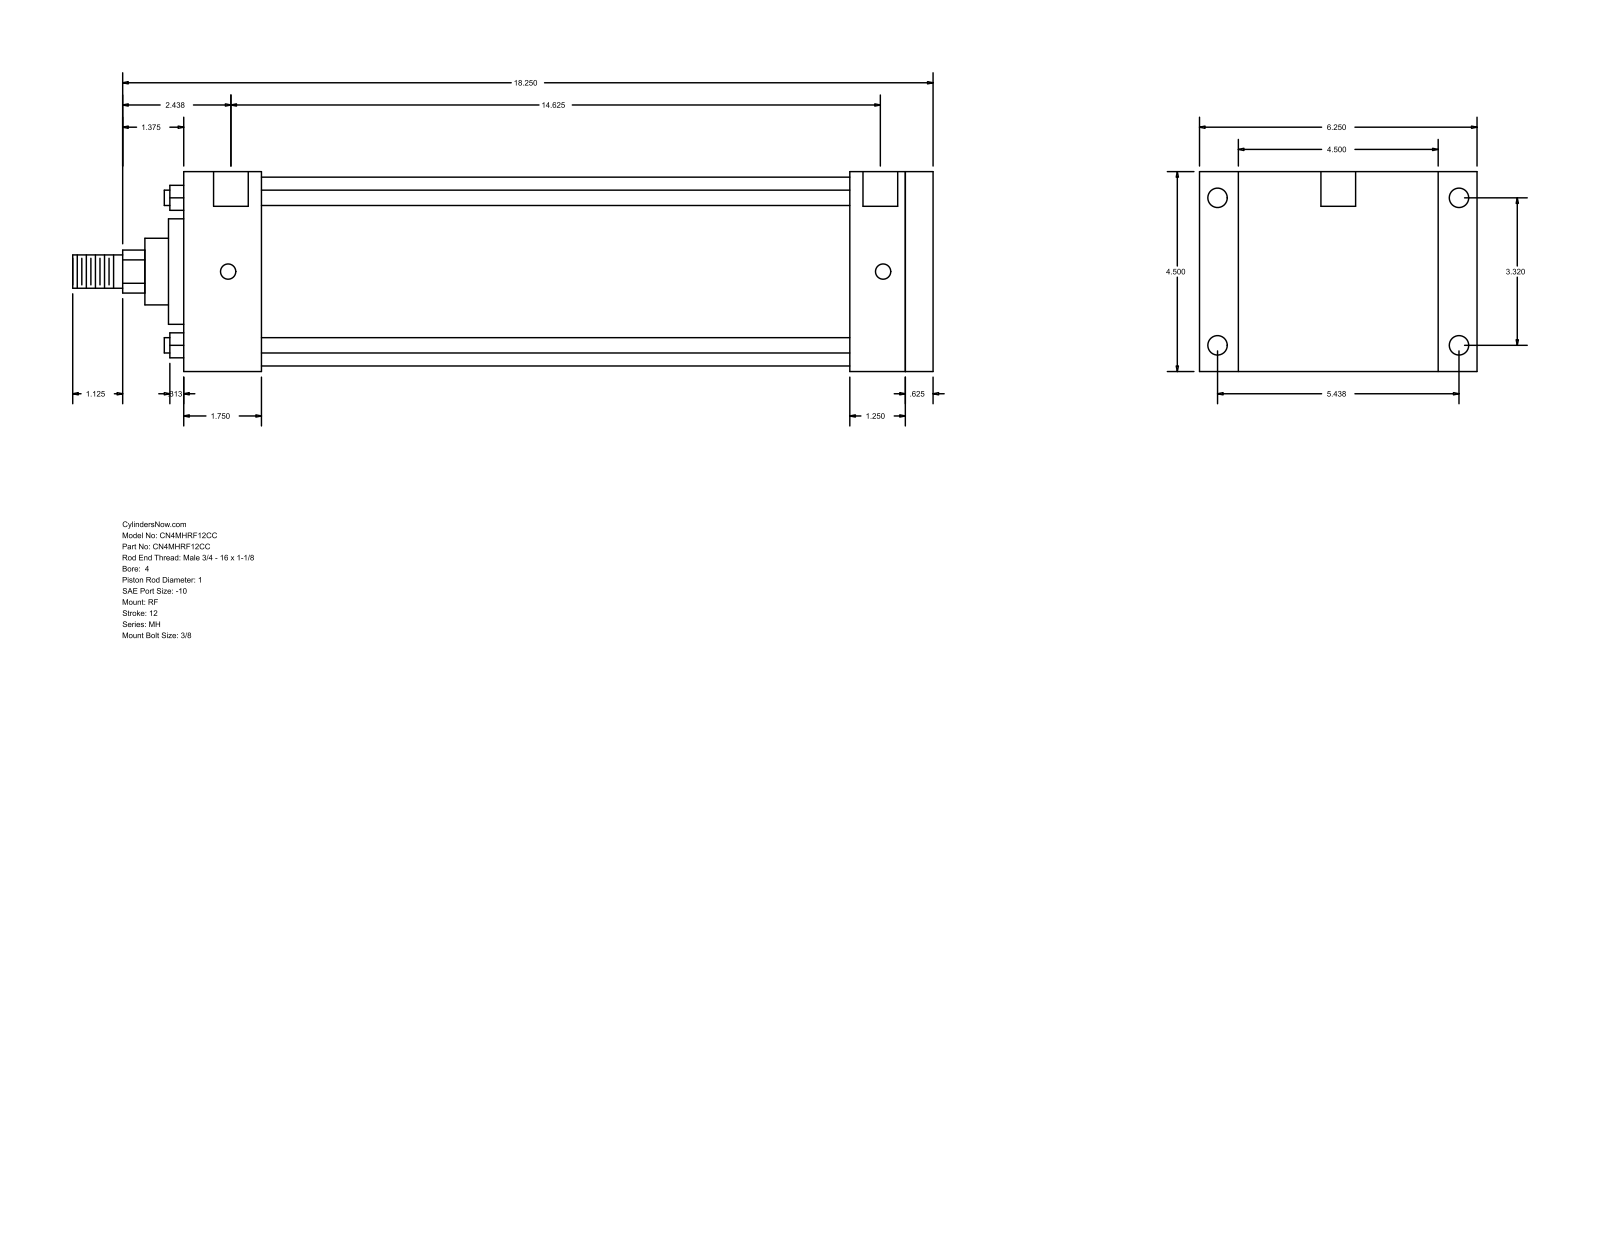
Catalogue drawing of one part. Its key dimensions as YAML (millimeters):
part_name: "MH_RF__0400_1"
step_written_by: "GSSL Pune (CONFIG_CONTROL_DESIGN)"
units: millimeters
bodies: {solids: 0, faces: 94, planar: 65, cylindrical: 29, other: 0}
overall_size: [492.12, 158.75, 114.3]
round_holes:
  - {diameter: 8.73, count: 4}
  - {diameter: 11.13, count: 4}
  - {diameter: 19.84, count: 2}
round_bosses_or_shafts:
  - {diameter: 8.76, count: 4}
  - {diameter: 107.95, count: 1}
  - {diameter: 60.33, count: 1}
  - {diameter: 38.1, count: 1}
  - {diameter: 25.4, count: 1}
  - {diameter: 19.05, count: 1}
partial_cylinders:
  - {radius: 12.29, count: 1}
face_to_face_distances: [114.3, 428.63, 412.76, 15.87, 44.46, 368.3, 384.17, 381.01, 336.55, 31.75]
hole_center_spacings: [84.32, 138.12, 161.82, 374.65, 1.58, 1.59, 371.48, 373.06]
